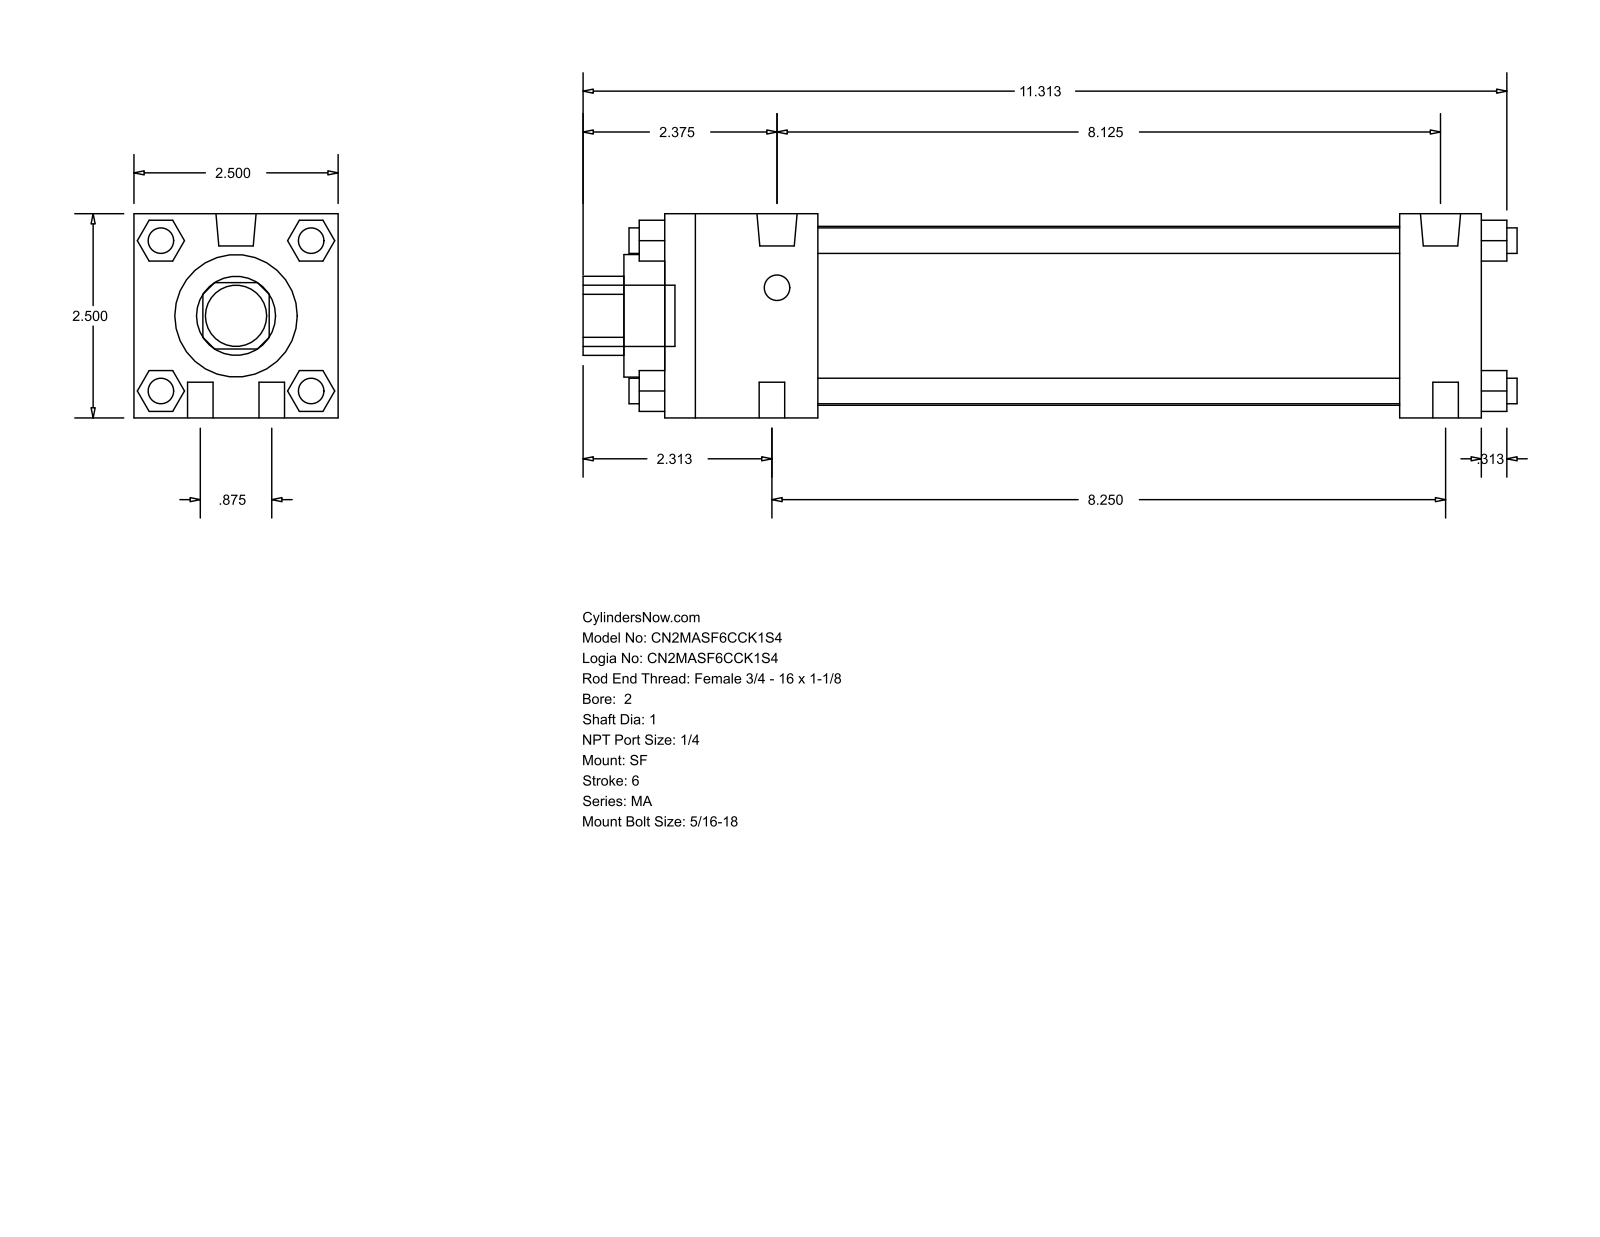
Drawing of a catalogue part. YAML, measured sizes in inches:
part_name: "MA_SF__0200_1"
step_written_by: "GSSL Pune (CONFIG_CONTROL_DESIGN)"
units: inches
bodies: {solids: 0, faces: 124, planar: 94, cylindrical: 30, other: 0}
overall_size: [11.437, 2.5, 2.5]
round_holes:
  - {diameter: 1, count: 1}
  - {diameter: 1.5, count: 1}
  - {diameter: 2.19, count: 1}
round_bosses_or_shafts:
  - {diameter: 0.313, count: 10}
  - {diameter: 0.492, count: 2}
  - {diameter: 0.75, count: 1}
partial_cylinders:
  - {radius: 0.484, count: 1}
face_to_face_distances: [2.5, 10, 0.5, 1, 9, 1.875, 7.125, 8.125, 1.593, 0.92]
